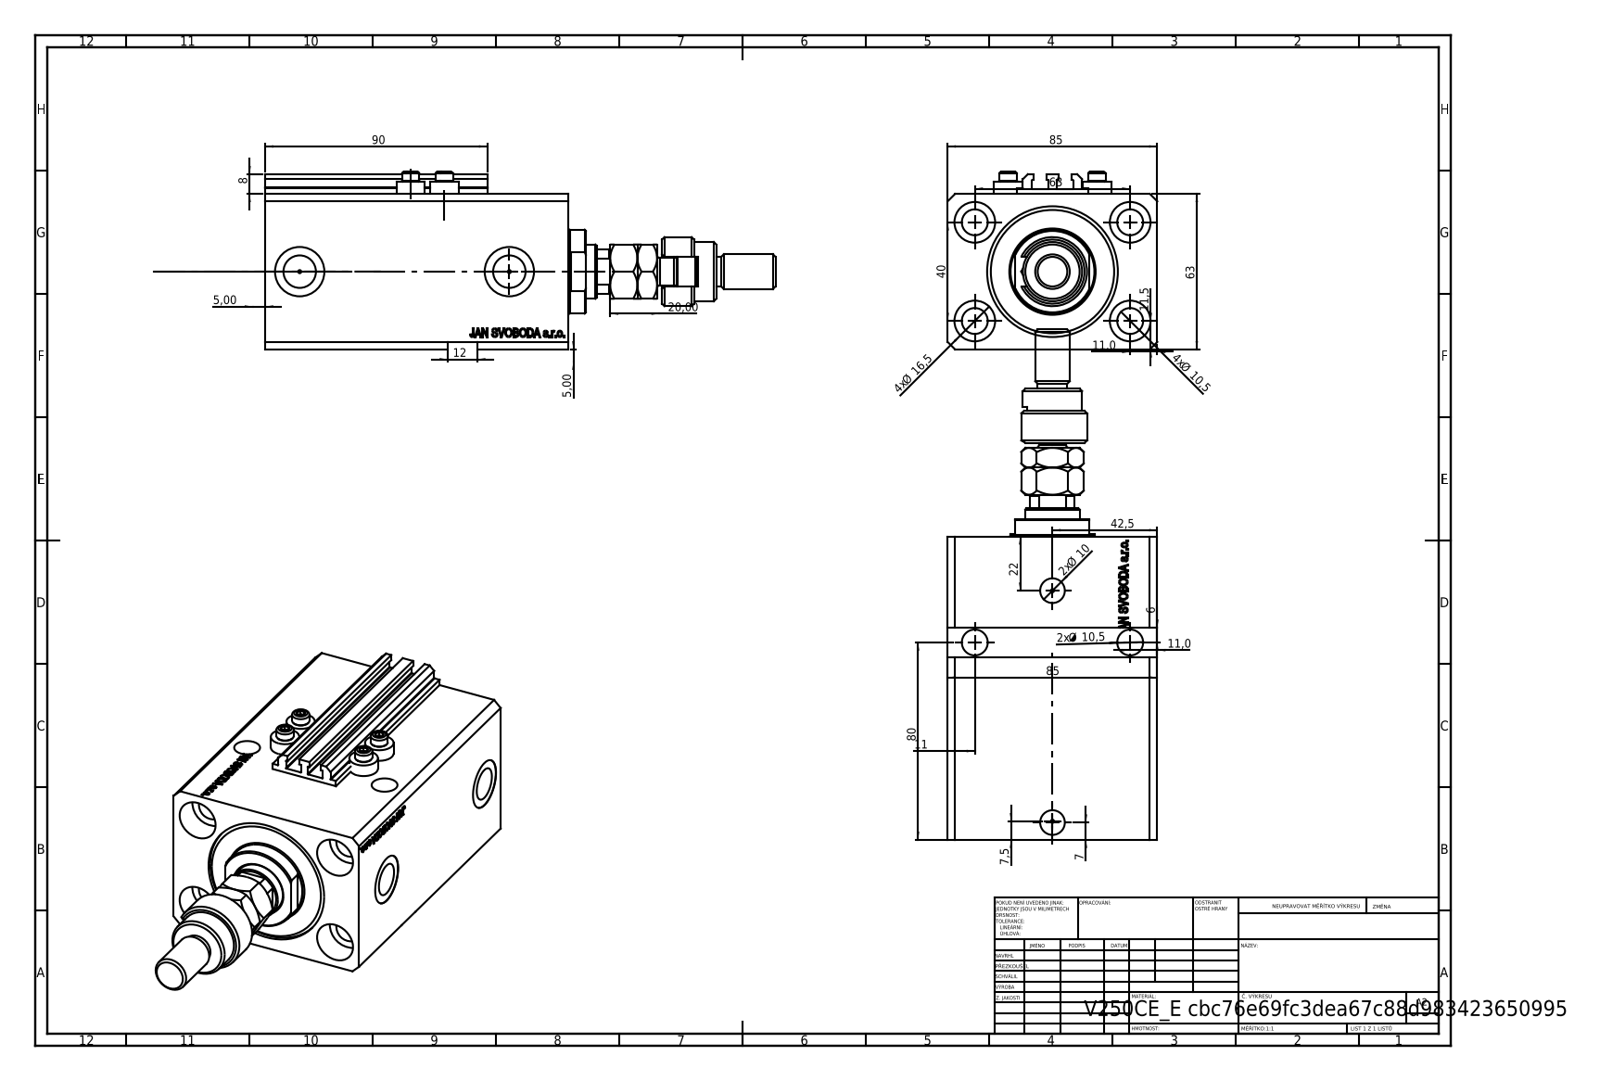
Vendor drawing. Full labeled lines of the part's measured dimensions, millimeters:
Part name (STEP PRODUCT): V250CE_E; ALLEN BOLT V250CE; V250CE_C_VCP; MFA (+2 more)
STEP written by: SolidWorks 2019 (CONFIG_CONTROL_DESIGN)
Units: millimetres
Bodies: 10 solids, 1188 faces (567 planar, 151 cylindrical, 470 other)
Overall size (bounding box): 206.9 × 85 × 72
Volume: 582 740 mm³ · Surface area: 128 537 mm²
Round holes (diameter × count): ⌀10.5 ×6, ⌀1.25 ×4, ⌀4 ×4, ⌀16.5 ×4, ⌀10 ×2, ⌀13.16 ×2, ⌀20 ×2, ⌀12.5 ×1, ⌀22 ×1, ⌀40 ×1, ⌀53 ×1
Round bosses / shafts (diameter × count): ⌀11.6 ×4, ⌀7 ×4, ⌀34 ×1, ⌀28 ×1, ⌀24 ×1, ⌀18 ×1, ⌀14 ×1, ⌀12 ×1
Partial cylindrical surfaces — rounded edges, fillets, slot ends (radius × count): R0.2 ×10, R9.75 ×1, R10.5 ×1
Main face-to-face distances: 63, 85, 123, 95.9, 27.1, 11.4, 84.5, 111.6, 3, 65
Hole centre spacings: 37.31, 63, 13.6, 15.4, 24.96, 33.62, 36, 37.86
